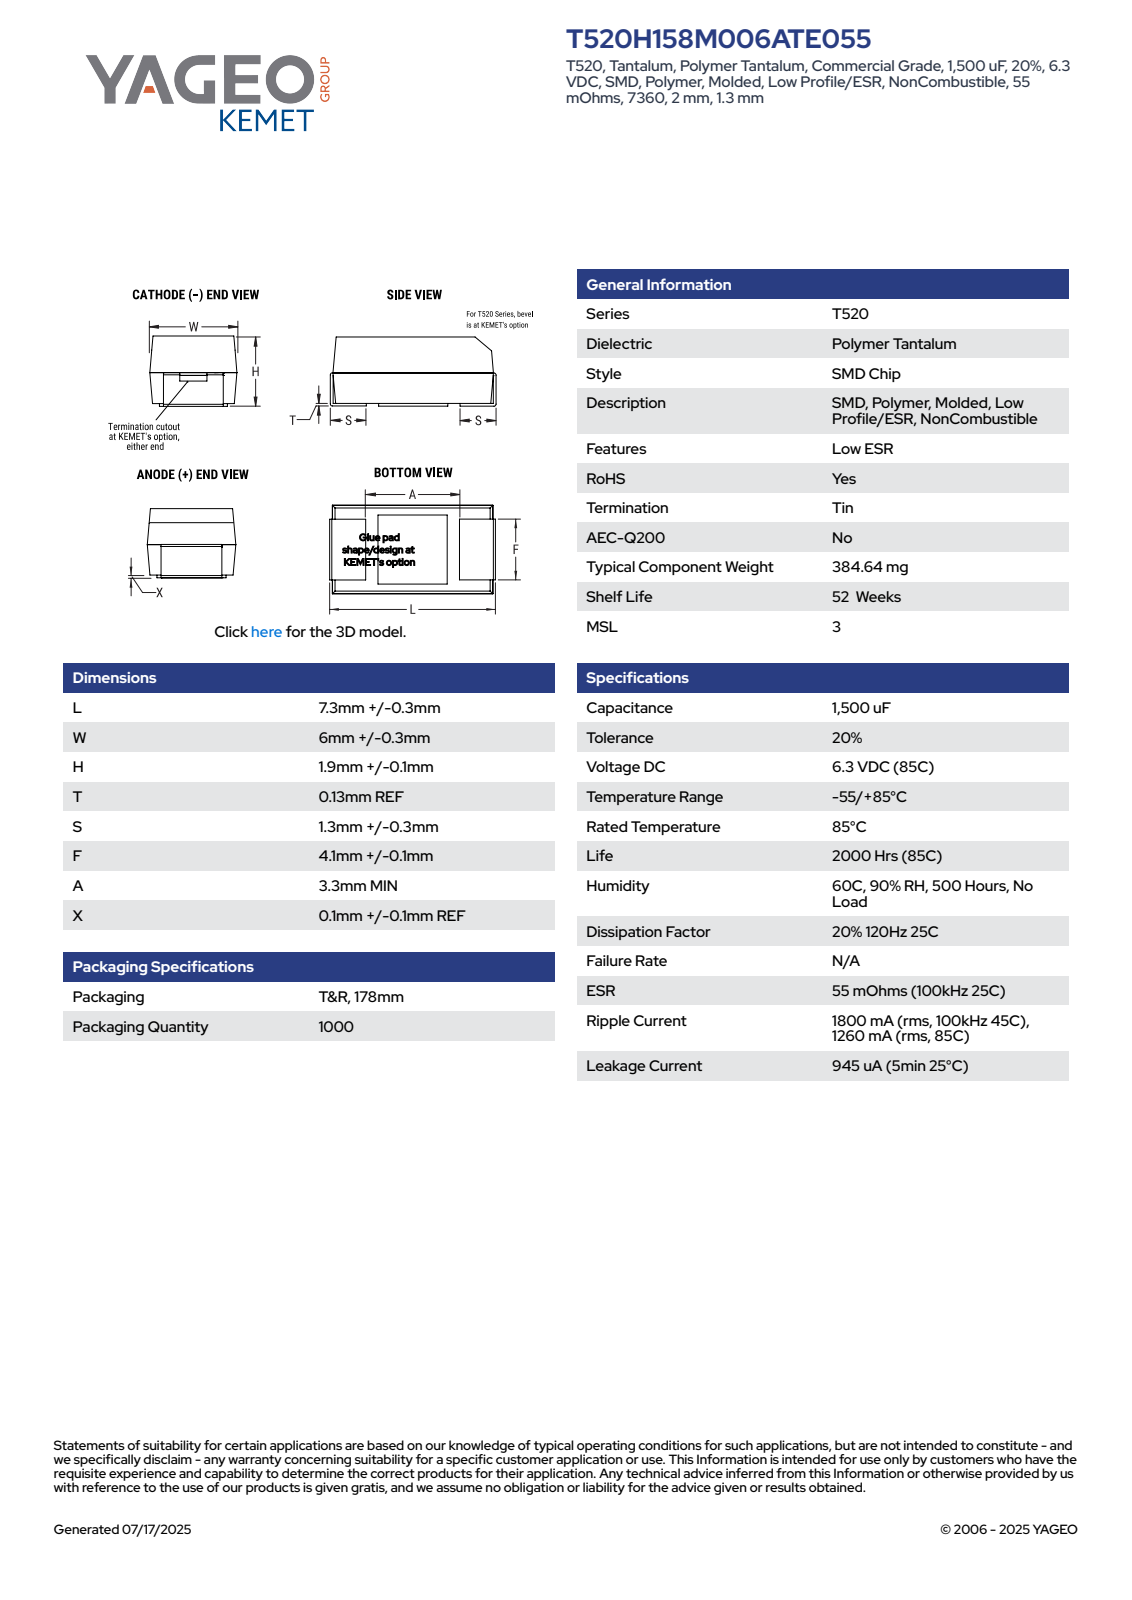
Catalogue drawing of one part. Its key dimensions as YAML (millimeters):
part_name: "CTS_TCM2NOBNOKBOPT_7360_L7.6W6.3H2T0.13S1.3F4.2A3.3X0.05"
step_written_by: "SolidWorks 2014 (AUTOMOTIVE_DESIGN)"
units: millimeters
bodies: {solids: 4, faces: 90, planar: 86, cylindrical: 4, other: 0}
overall_size: [7.6, 6.3, 2]
volume: 85
surface_area: 159
partial_cylinders:
  - {radius: 0.13, count: 4}
face_to_face_distances: [1.92, 1.87, 7.17, 2, 6.15, 6.14, 7.47, 7.34, 7.6, 1.3]
